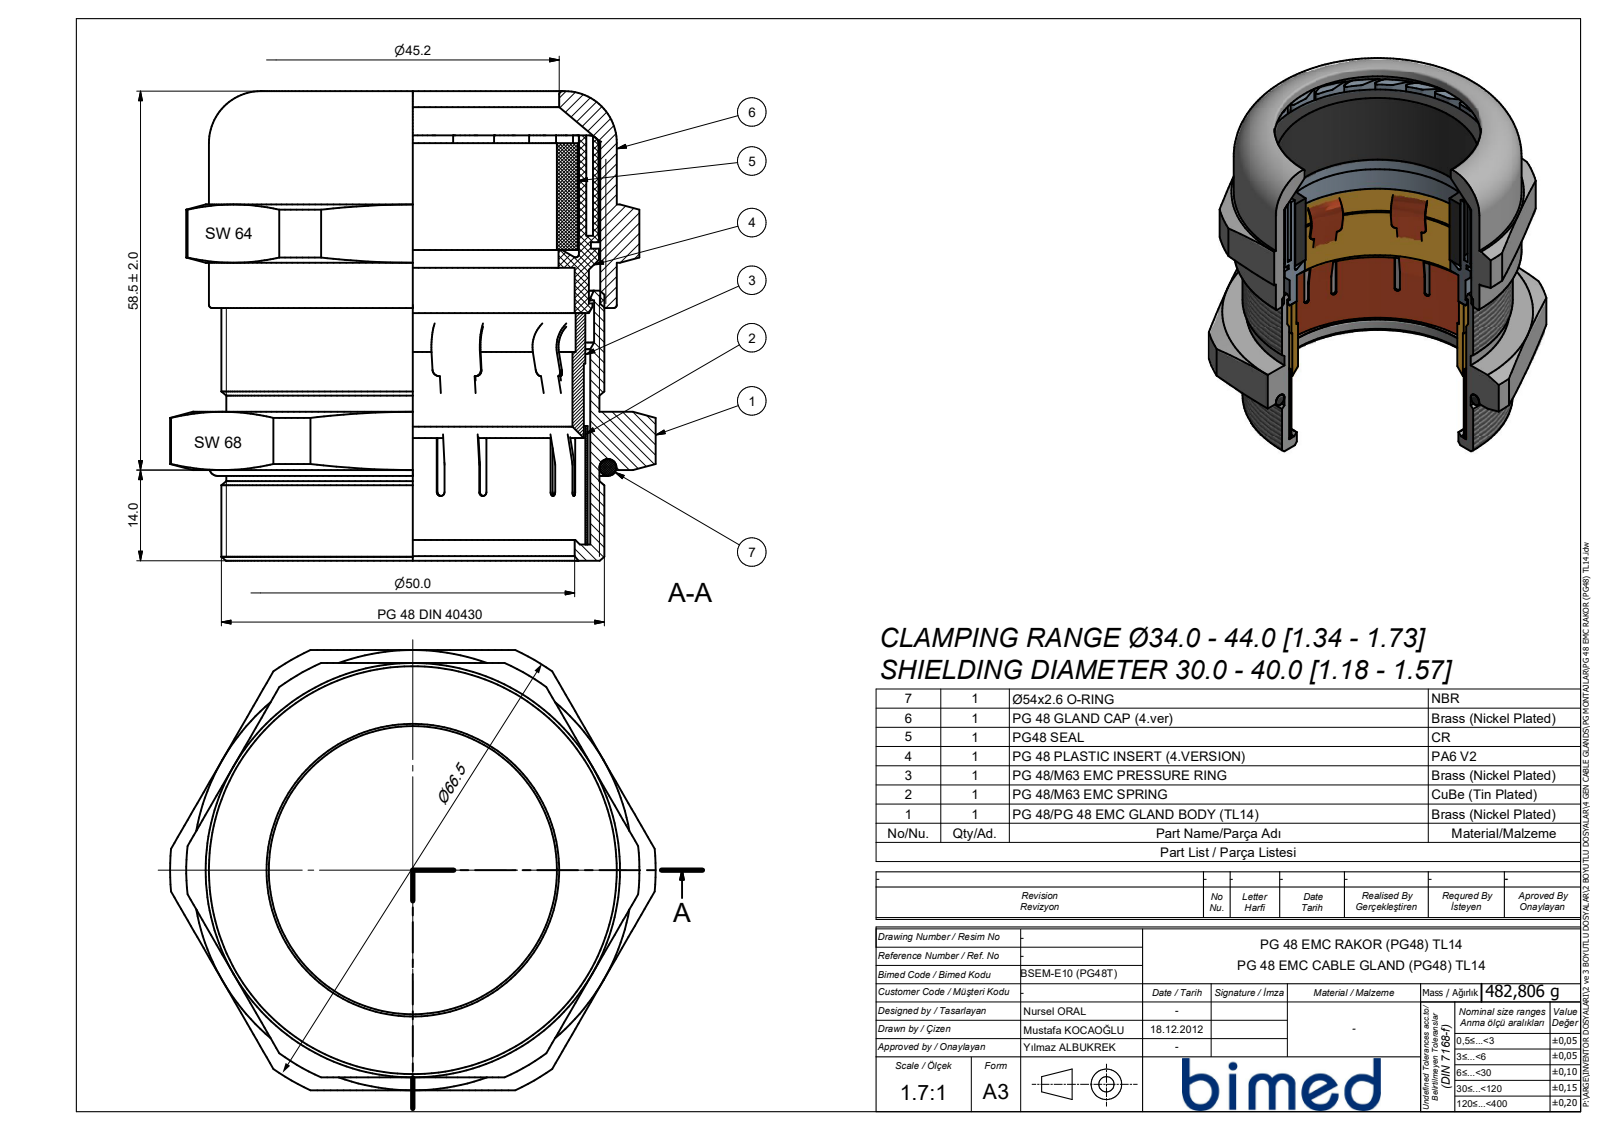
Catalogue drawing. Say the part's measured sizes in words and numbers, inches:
The part is named "BSEM-E10-PG48T-WCL". Its 3-D file was written by "SolidWorks 2021 (CONFIG_CONTROL_DESIGN)". It is 1 solid with 86 faces: 20 planar, 26 cylindrical and 40 other. Overall it measures 2.953 by 2.855 by 2.677 inches. Its volume is 13.59 cubic inches and its surface area 36.09 square inches. Round bosses or shafts: 1 of diameter 2.48, 1 of diameter 2.329, 1 of diameter 2.269. Partial cylindrical surfaces (rounded edges, fillets, slot ends): 1 of radius 1.378, 1 of radius 1.476. The main face-to-face distances are 2.855, 0.079, 2.598, 0.906, 1.95, 2.677, 2.52, 0.354, 0.551, 2.304.
